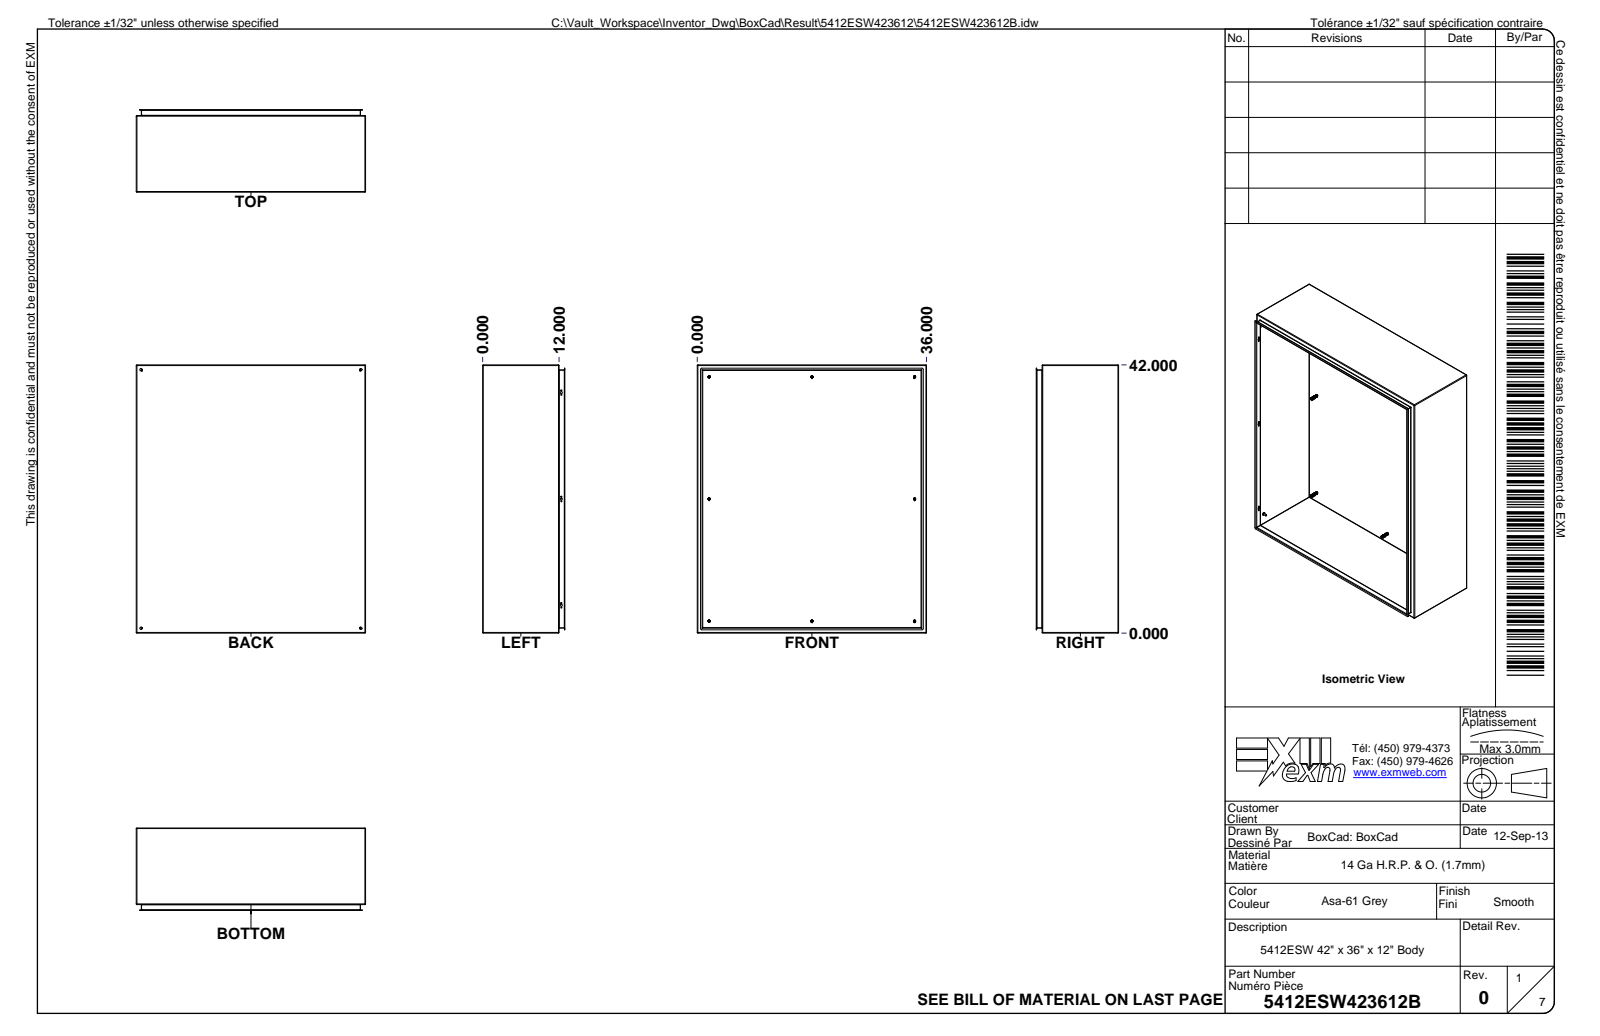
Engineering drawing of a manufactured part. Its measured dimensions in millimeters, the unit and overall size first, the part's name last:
Units: millimetres
Overall size (bounding box): 1066.8 × 914.9 × 337.7
Round holes (diameter × count): ⌀0.8 ×30, ⌀8 ×28, ⌀5.1 ×26, ⌀7.4 ×24, ⌀5 ×20, ⌀7 ×20, ⌀9.5 ×20, ⌀1.1 ×12, ⌀4.4 ×8, ⌀6.9 ×8, ⌀4.5 ×6, ⌀9.9 ×4
Round bosses / shafts (diameter × count): ⌀0.8 ×29, ⌀5.9 ×27, ⌀9 ×20, ⌀1 ×12, ⌀18.2 ×8, ⌀7.9 ×8, ⌀6.9 ×8, ⌀6.7 ×8
Partial cylindrical surfaces — rounded edges, fillets, slot ends (radius × count): R0.5 ×553, R0.3 ×201, R1 ×188, R0.8 ×150, R0.2 ×140, R2.2 ×108, R0.4 ×84, R0.3 ×74
Main face-to-face distances: 1.7, 23.9, 22.2, 26.6, 24.9, 2.7, 323.7, 322, 299.8, 297.1
Hole centre spacings: 423, 998, 8.9, 18.7, 26.7, 35.2, 330.2, 393.7
Volume: 13 030 000 mm³ · Surface area: 9 443 000 mm²
Bodies: 161 solids, 25856 faces (11239 planar, 5710 cylindrical, 8907 other)
Part name (STEP PRODUCT): 5412ESW423612; 5412ESW423612B; 5412ESW423612B-P; STK-Q-16005 (+8 more)
STEP written by: Autodesk Inventor 2024 (AUTOMOTIVE_DESIGN)
